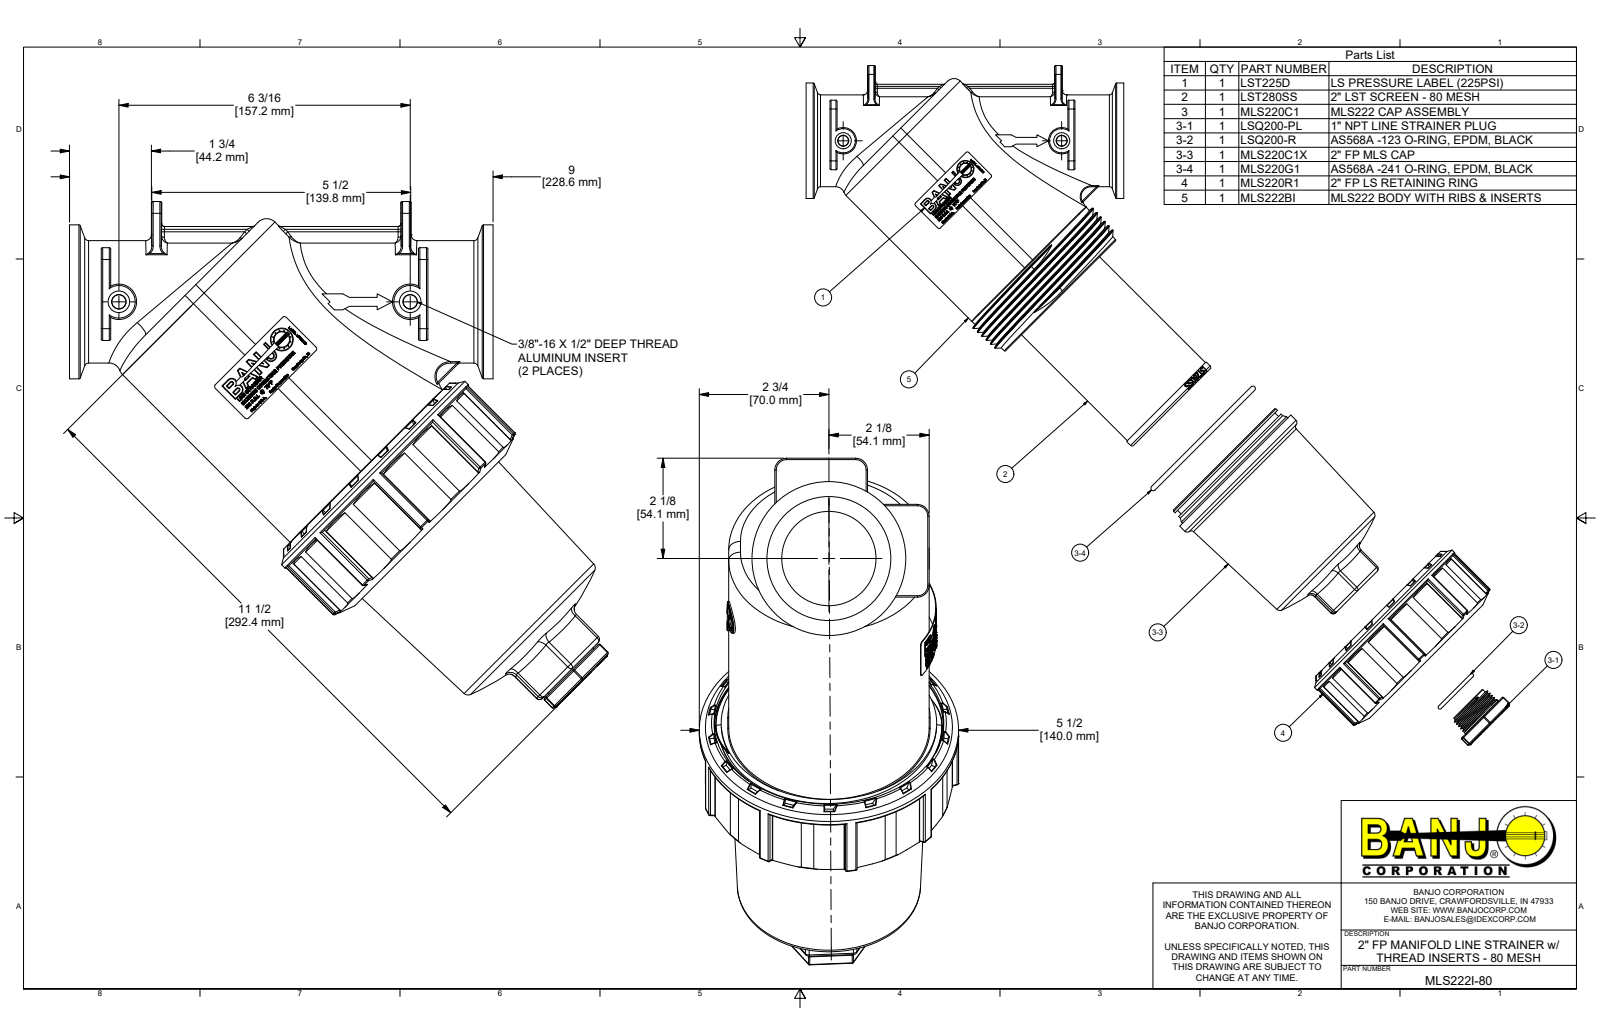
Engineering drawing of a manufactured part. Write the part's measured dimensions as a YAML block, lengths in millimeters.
part_name: "MLS222i-80; MLS222BI; MLS222B; V25022H (+8 more)"
step_written_by: "Autodesk Inventor 2022 (AUTOMOTIVE_DESIGN)"
units: millimeters
bodies: {solids: 11, faces: 3961, planar: 1739, cylindrical: 570, other: 1652}
overall_size: [290.8, 273.3, 140]
volume: 1485000
surface_area: 483300
round_holes:
  - {diameter: 7.5, count: 2}
  - {diameter: 7.8, count: 2}
  - {diameter: 8.3, count: 1}
  - {diameter: 11.5, count: 1}
  - {diameter: 11.7, count: 1}
  - {diameter: 16.3, count: 1}
  - {diameter: 19.1, count: 1}
  - {diameter: 25.4, count: 1}
  - {diameter: 29.9, count: 1}
  - {diameter: 50.8, count: 1}
  - {diameter: 66.8, count: 1}
  - {diameter: 74.6, count: 1}
round_bosses_or_shafts:
  - {diameter: 81, count: 2}
  - {diameter: 11.6, count: 2}
  - {diameter: 140, count: 1}
  - {diameter: 133.4, count: 1}
  - {diameter: 113, count: 1}
  - {diameter: 107.1, count: 1}
  - {diameter: 104.1, count: 1}
  - {diameter: 99.2, count: 1}
partial_cylinders:
  - {radius: 0.8, count: 76}
  - {radius: 0.3, count: 36}
  - {radius: 1.5, count: 16}
  - {radius: 2.3, count: 12}
  - {radius: 6.4, count: 8}
  - {radius: 3.2, count: 6}
  - {radius: 0.8, count: 4}
  - {radius: 3, count: 3}
face_to_face_distances: [2.5, 226.1, 7.6, 228.6, 147.5, 155.2, 134.6, 16.5, 5.1, 171.2]
hole_center_spacings: [34.3, 64.1, 72.2, 90.3, 106.5, 157.2]
